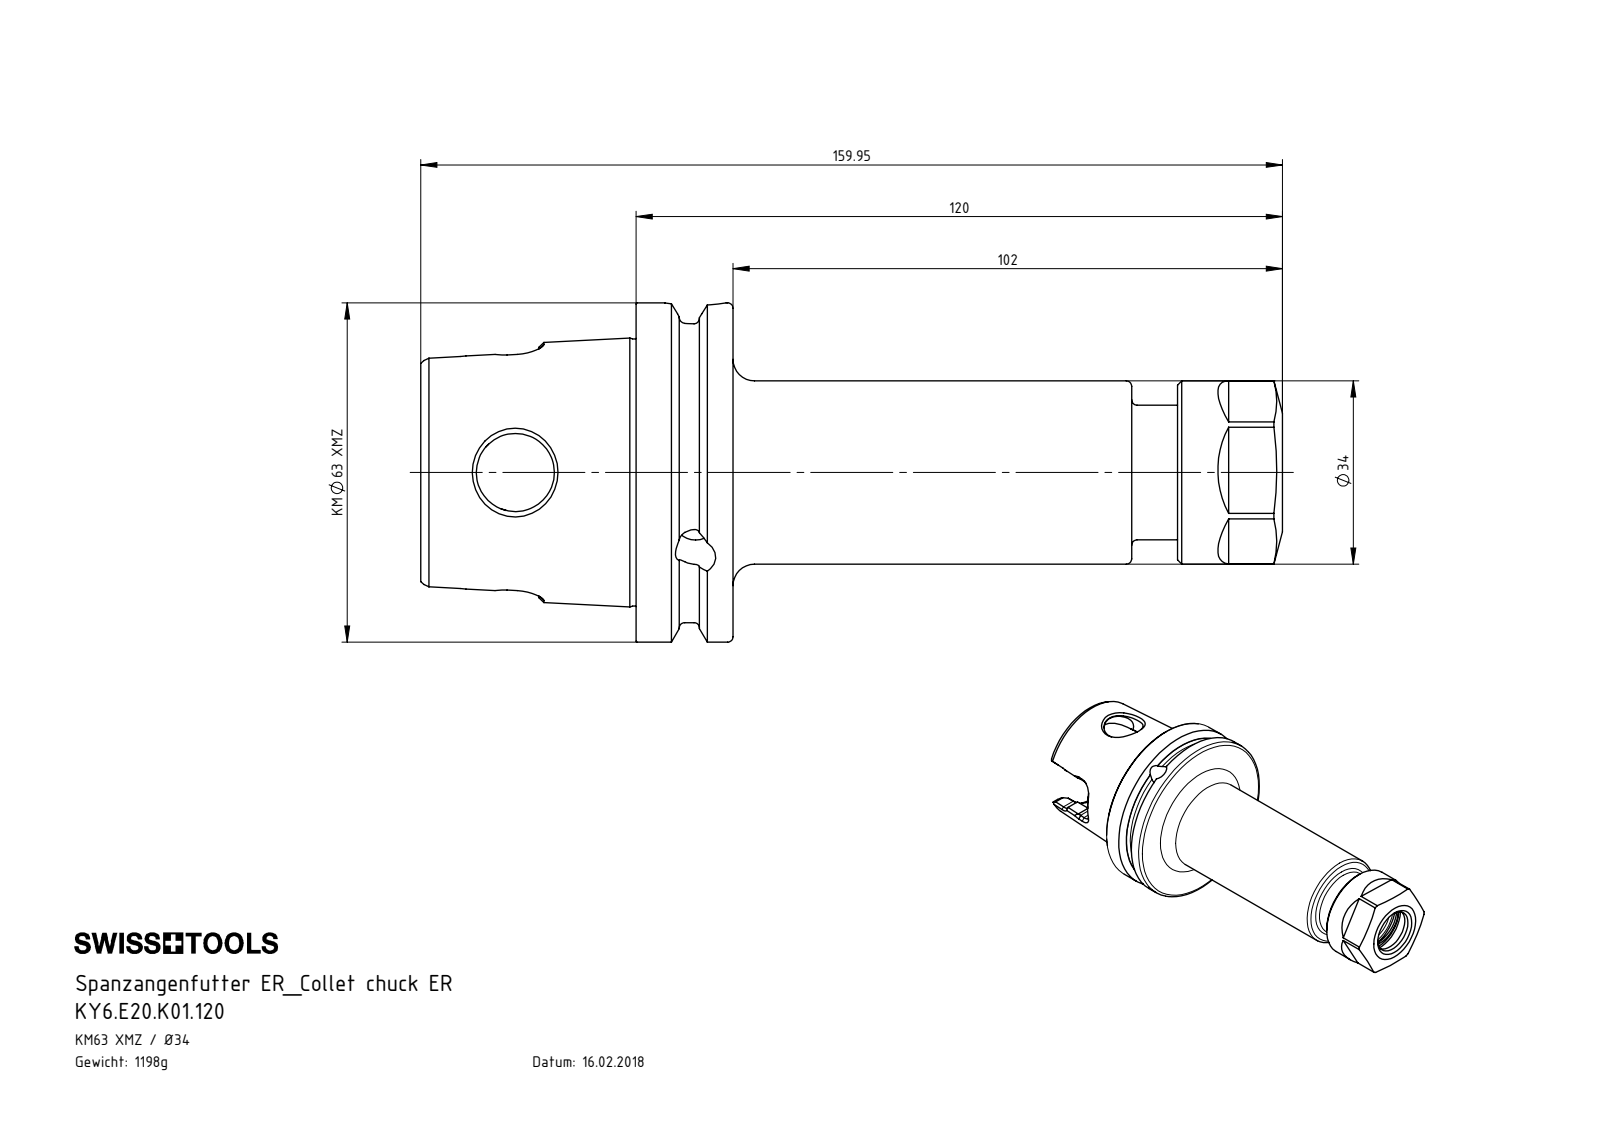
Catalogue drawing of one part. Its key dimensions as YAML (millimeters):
part_name: "KY6.E20.K01.120; ERU-AN5.K01.020_A; E20-ER2.001.020; KY6-E20.K01.120_B"
step_written_by: "SolidWorks 2017 (CONFIG_CONTROL_DESIGN)"
units: millimeters
bodies: {solids: 3, faces: 319, planar: 97, cylindrical: 72, other: 150}
overall_size: [159.95, 62.95, 62.95]
volume: 152646
surface_area: 38086
round_holes:
  - {diameter: 7.47, count: 2}
  - {diameter: 6, count: 1}
  - {diameter: 8, count: 1}
  - {diameter: 8.48, count: 1}
  - {diameter: 10, count: 1}
  - {diameter: 10.2, count: 1}
  - {diameter: 11.5, count: 1}
  - {diameter: 13.5, count: 1}
  - {diameter: 14.5, count: 1}
  - {diameter: 15.9, count: 1}
  - {diameter: 23.5, count: 1}
  - {diameter: 25.5, count: 1}
round_bosses_or_shafts:
  - {diameter: 62.95, count: 1}
  - {diameter: 55.7, count: 1}
  - {diameter: 34, count: 1}
  - {diameter: 25, count: 1}
  - {diameter: 12, count: 1}
  - {diameter: 11, count: 1}
partial_cylinders:
  - {radius: 4, count: 6}
  - {radius: 7.04, count: 2}
  - {radius: 9.6, count: 2}
face_to_face_distances: [18, 1.1, 19.1, 101.6, 100.5, 82.5, 6, 30, 93.1, 92]
